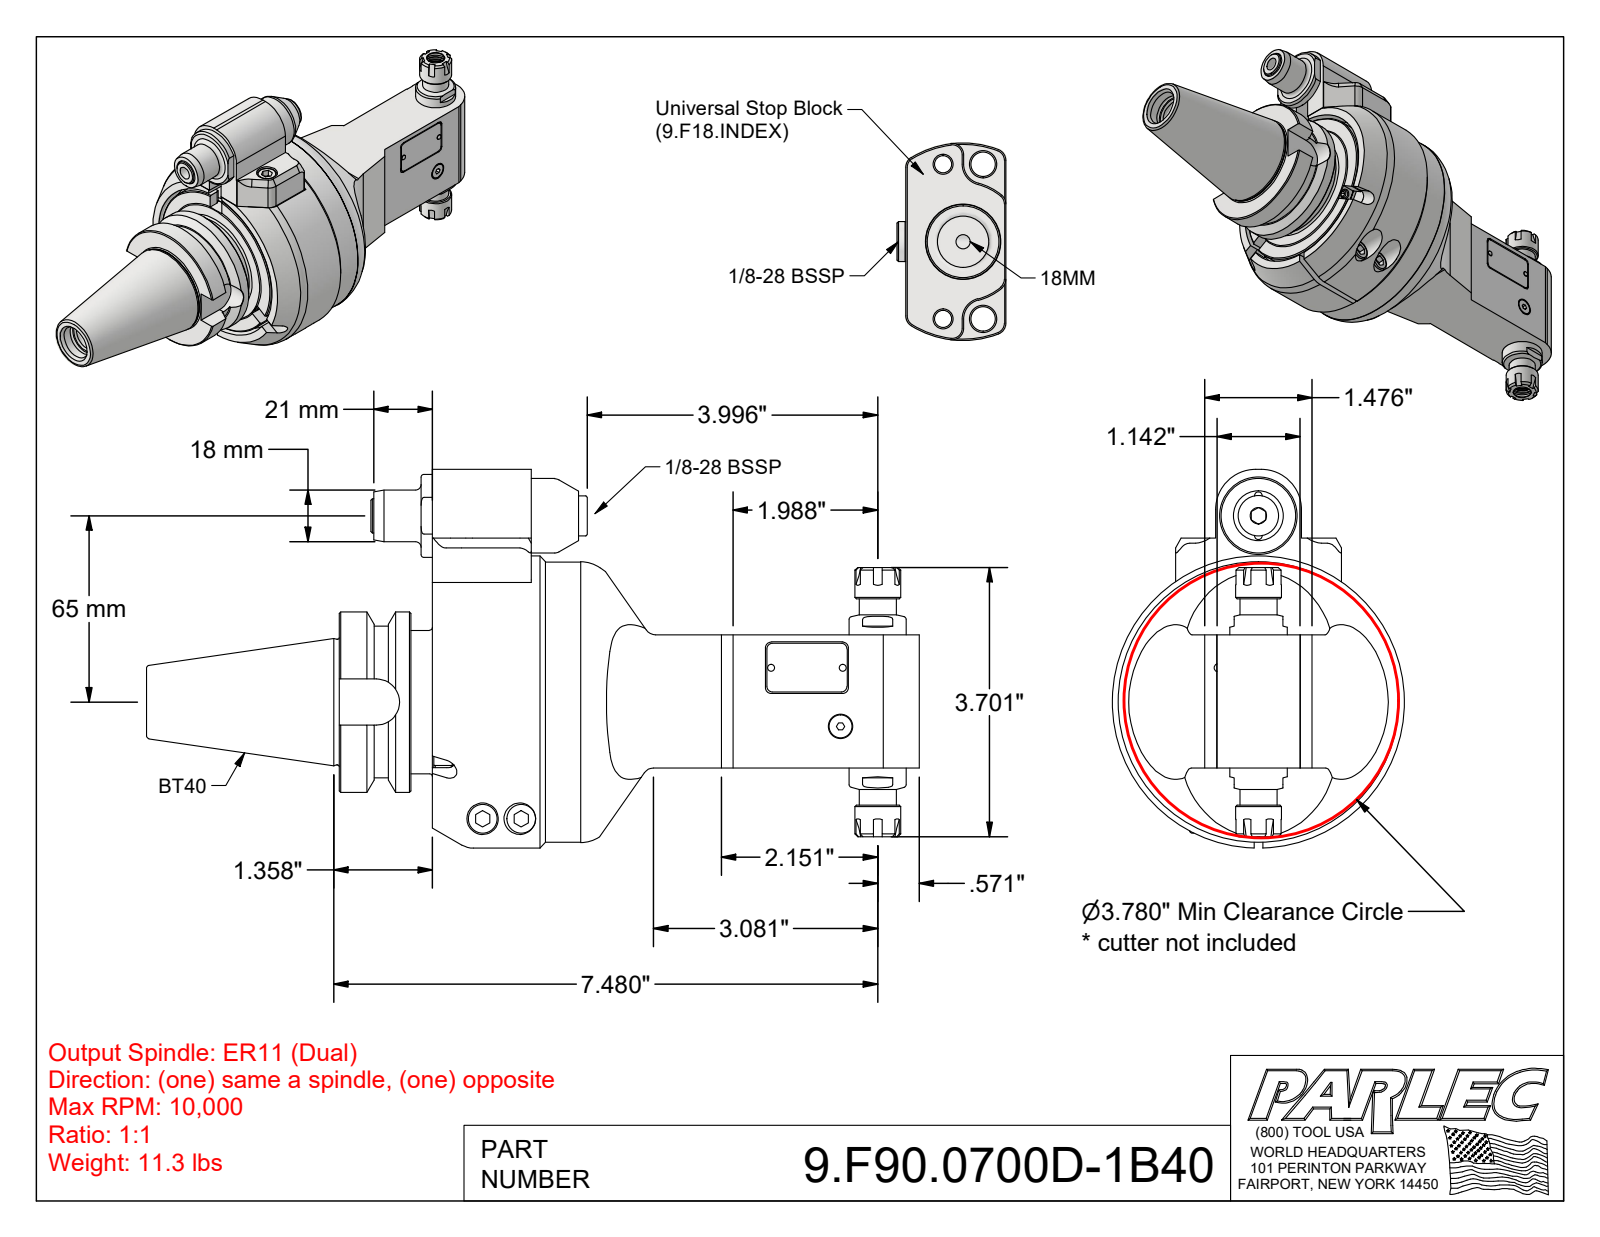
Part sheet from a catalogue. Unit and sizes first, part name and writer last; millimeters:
Units: millimetres
Overall size (bounding box): 269.9 × 132.2 × 102
Round holes (diameter × count): ⌀8.5 ×21, ⌀2.6 ×2, ⌀4.2 ×2, ⌀5 ×2, ⌀10.4 ×2, ⌀10.5 ×2, ⌀11 ×2, ⌀2.5 ×1, ⌀3 ×1, ⌀6.5 ×1, ⌀7 ×1, ⌀7.5 ×1
Round bosses / shafts (diameter × count): ⌀10 ×4, ⌀6 ×4, ⌀18 ×2, ⌀8 ×2, ⌀2.5 ×2, ⌀102 ×1, ⌀97.8 ×1, ⌀77 ×1
Partial cylindrical surfaces — rounded edges, fillets, slot ends (radius × count): R2 ×12, R30 ×12, R4 ×4, R0.5 ×2, R1 ×2, R3.5 ×2, R5 ×2, R14 ×2
Main face-to-face distances: 32, 39.5, 0.5, 7.5, 7, 46.5, 8, 64.7, 18.3, 32.5
Hole centre spacings: 38.5, 76.3, 46.3, 54.5, 10.7, 37.3, 74, 61.5
Volume: 824 100 mm³ · Surface area: 144 300 mm²
Bodies: 5 solids, 553 faces (261 planar, 152 cylindrical, 140 other)
Part name (STEP PRODUCT): 9.F90.0700D-1B40; 9_GA1_346_2 (Type 1, BT40, 65mm); 9_F90_07000_2U
STEP written by: Autodesk Inventor 2022 (AUTOMOTIVE_DESIGN)
